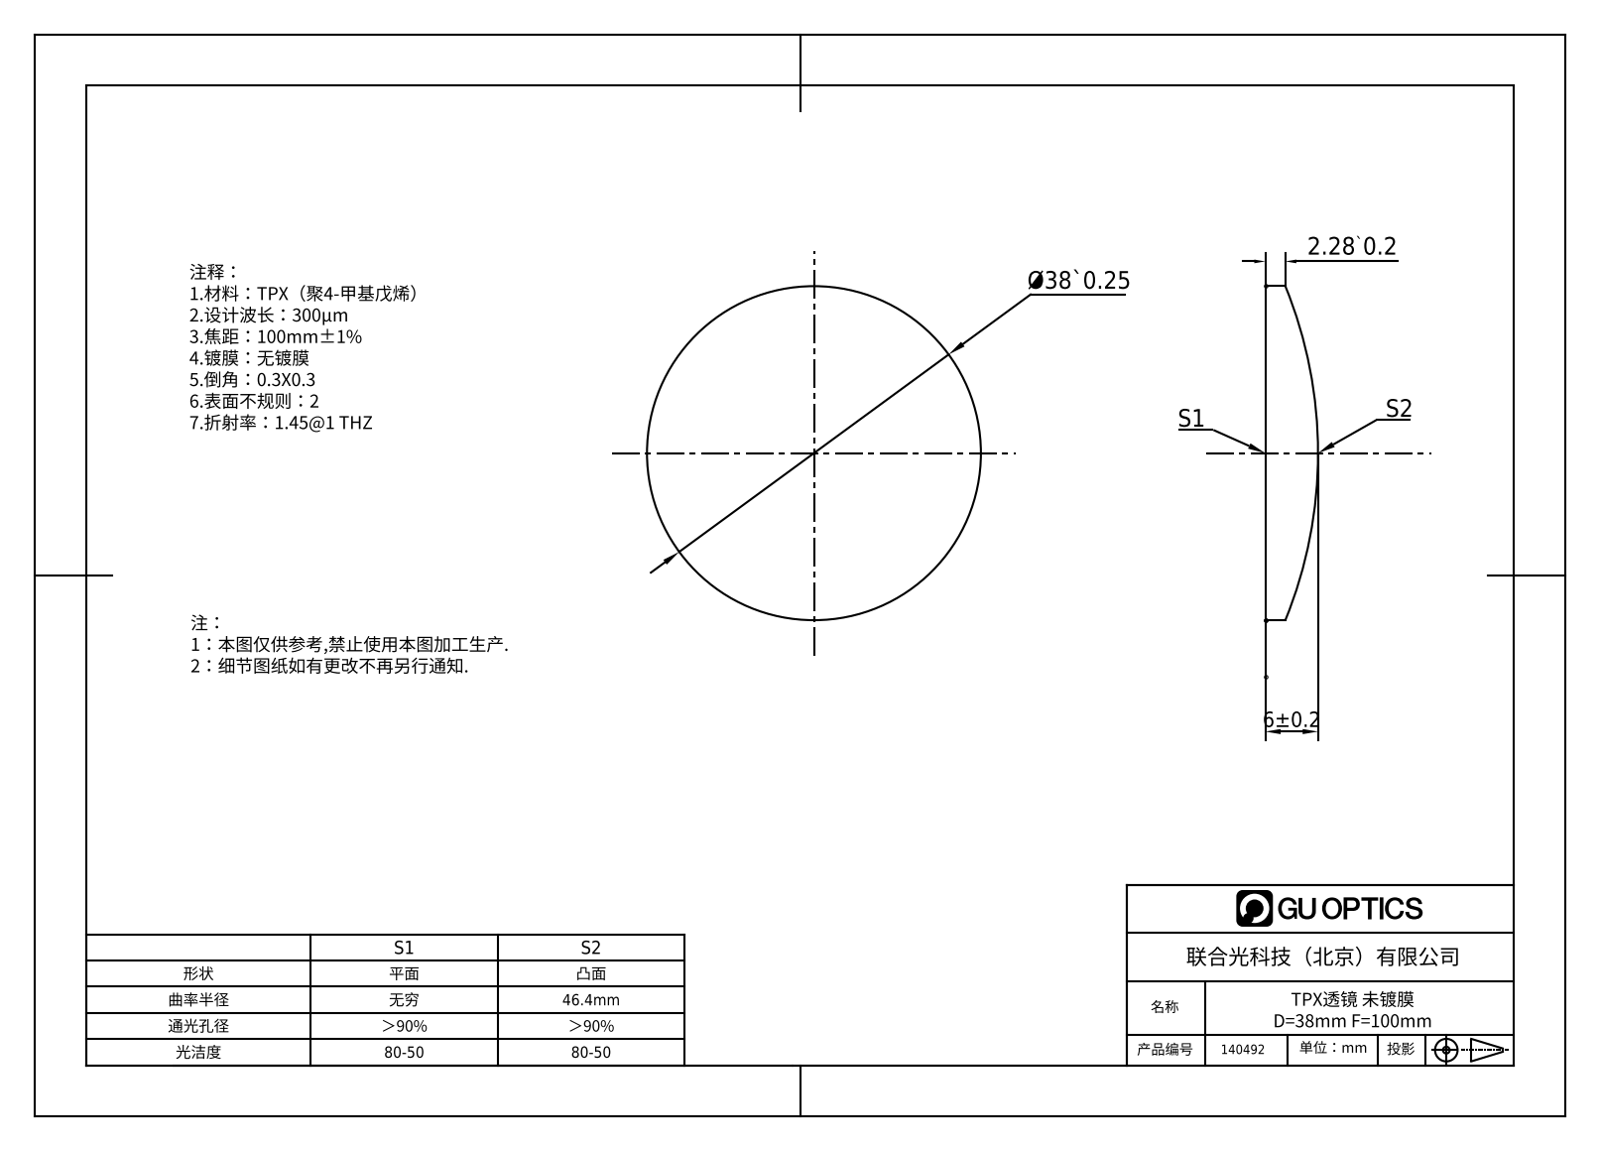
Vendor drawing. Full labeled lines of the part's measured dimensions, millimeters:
Part name (STEP PRODUCT): 140492
STEP written by: SolidWorks 2020 (AUTOMOTIVE_DESIGN)
Units: millimetres
Bodies: 1 solid, 5 faces (1 planar, 2 cylindrical, 2 other)
Overall size (bounding box): 37.99 × 37.99 × 6
Volume: 4 721 mm³ · Surface area: 2 583 mm²
Round bosses / shafts (diameter × count): ⌀37.99 ×1
